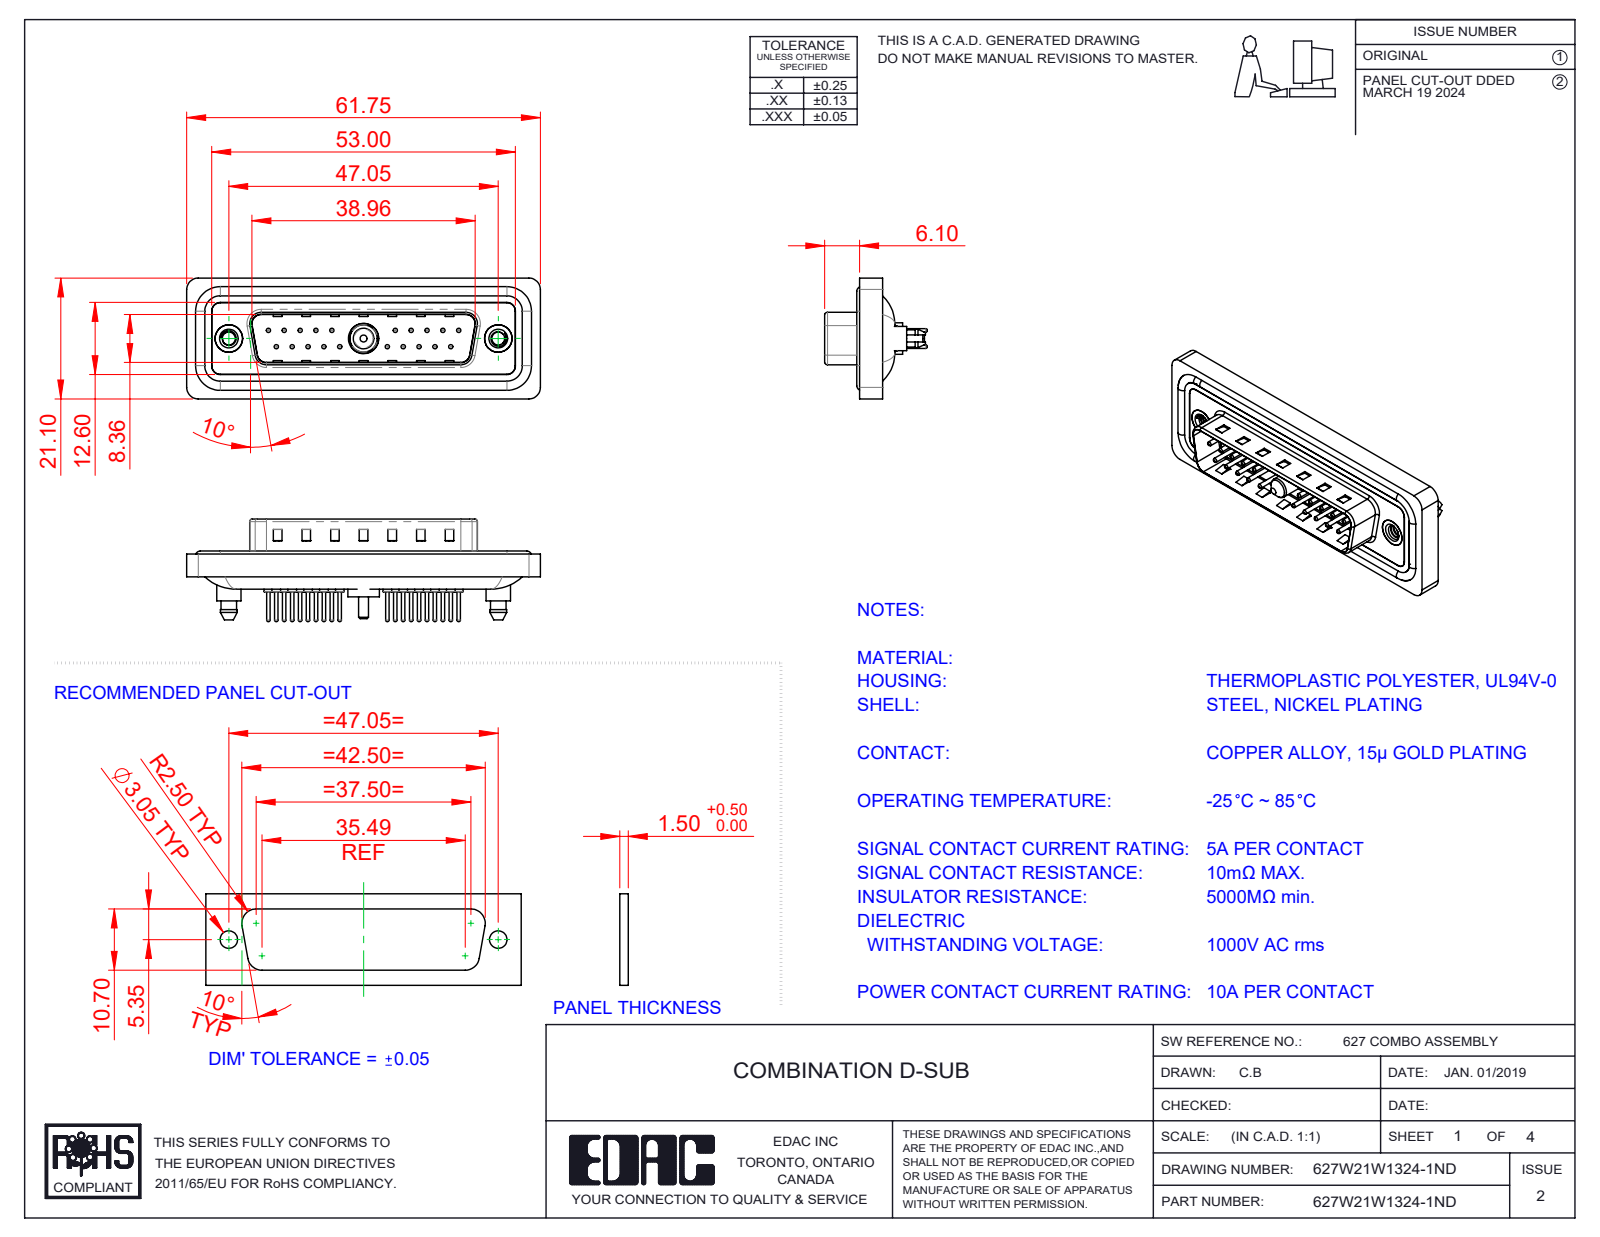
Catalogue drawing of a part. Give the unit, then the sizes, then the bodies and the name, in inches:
Units: inches
Overall size (bounding box): 2.431 × 0.831 × 0.705
Round holes (diameter × count): ⌀0.03 ×20, ⌀0.063 ×20, ⌀0.079 ×20, ⌀0.089 ×2, ⌀0.157 ×2, ⌀0.189 ×2, ⌀0.197 ×2, ⌀0.191 ×1, ⌀0.209 ×1
Round bosses / shafts (diameter × count): ⌀0.059 ×20, ⌀0.024 ×20, ⌀0.063 ×4, ⌀0.213 ×2, ⌀0.193 ×2, ⌀0.167 ×2, ⌀0.217 ×1, ⌀0.205 ×1
Partial cylindrical surfaces — rounded edges, fillets, slot ends (radius × count): R0.059 ×24, R0.079 ×18, R0.063 ×10, R0.02 ×8, R0.01 ×4, R0.024 ×4, R0.026 ×4, R0.035 ×4
Main face-to-face distances: 0.016, 0.059, 0.043, 0.063, 0.02, 0.122, 0.114, 0.161, 0.032, 0.377
Hole centre spacings: 0.124, 0.109, 0.218, 0.327, 0.198, 0.763, 0.826, 0.872
Volume: 0.447 in³ · Surface area: 19.03 in²
Bodies: 29 solids, 1320 faces (375 planar, 527 cylindrical, 418 other)
Part name (STEP PRODUCT): Power Pin_10A S; 627Combo Shell Rear_25 Contacts; 627Combo Shell Front_25 Contacts; 627Combo Threaded Boardlock_5 (+6 more)
STEP written by: SolidWorks 2023 (CONFIG_CONTROL_DESIGN)
